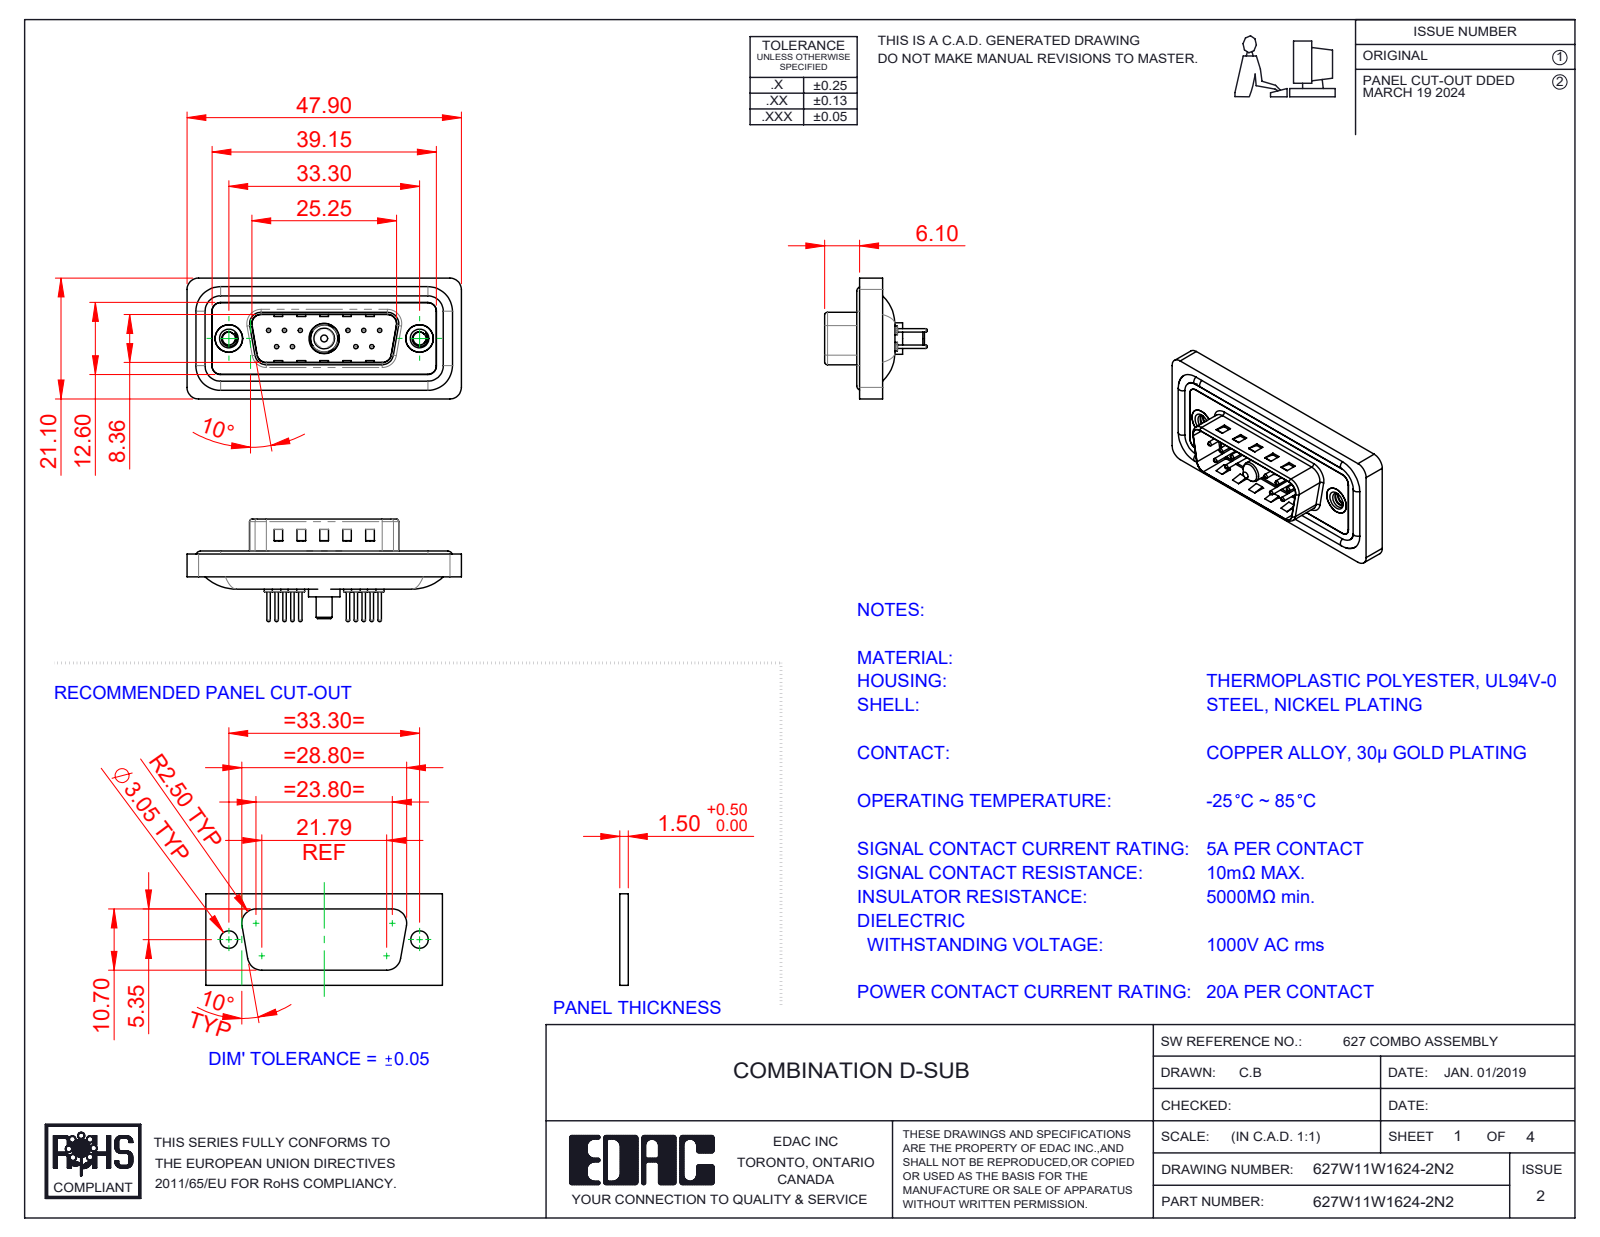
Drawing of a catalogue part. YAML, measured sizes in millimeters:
part_name: "627Combo Waterproof Housing_15 Contacts; 627Combo Shell Front_15 Contacts; 627W11W1624-2N2; Power Pin_20A S (+5 more)"
step_written_by: "SolidWorks 2023 (CONFIG_CONTROL_DESIGN)"
units: millimeters
bodies: {solids: 19, faces: 869, planar: 266, cylindrical: 347, other: 256}
overall_size: [47.9, 21.1, 17.9]
volume: 5448
surface_area: 8836
round_holes:
  - {diameter: 0.75, count: 10}
  - {diameter: 1.6, count: 10}
  - {diameter: 2, count: 10}
  - {diameter: 2.26, count: 2}
  - {diameter: 4, count: 2}
  - {diameter: 4.8, count: 2}
  - {diameter: 5, count: 2}
  - {diameter: 4.85, count: 1}
  - {diameter: 5.3, count: 1}
round_bosses_or_shafts:
  - {diameter: 1.5, count: 10}
  - {diameter: 0.6, count: 10}
  - {diameter: 1.6, count: 4}
  - {diameter: 4.9, count: 2}
  - {diameter: 5.5, count: 1}
  - {diameter: 5.2, count: 1}
  - {diameter: 4.75, count: 1}
  - {diameter: 3.75, count: 1}
partial_cylinders:
  - {radius: 1.5, count: 26}
  - {radius: 2, count: 20}
  - {radius: 0.5, count: 8}
  - {radius: 1.6, count: 8}
  - {radius: 1, count: 7}
  - {radius: 0.25, count: 4}
  - {radius: 0.6, count: 4}
  - {radius: 0.65, count: 4}
face_to_face_distances: [0.4, 1.1, 1.6, 1.5, 0.5, 2.9, 3.1, 2.5, 4.1, 0.82]
hole_center_spacings: [3.16, 2.77, 13.85, 11.08, 16.62, 5.03, 5.04, 5.54]
